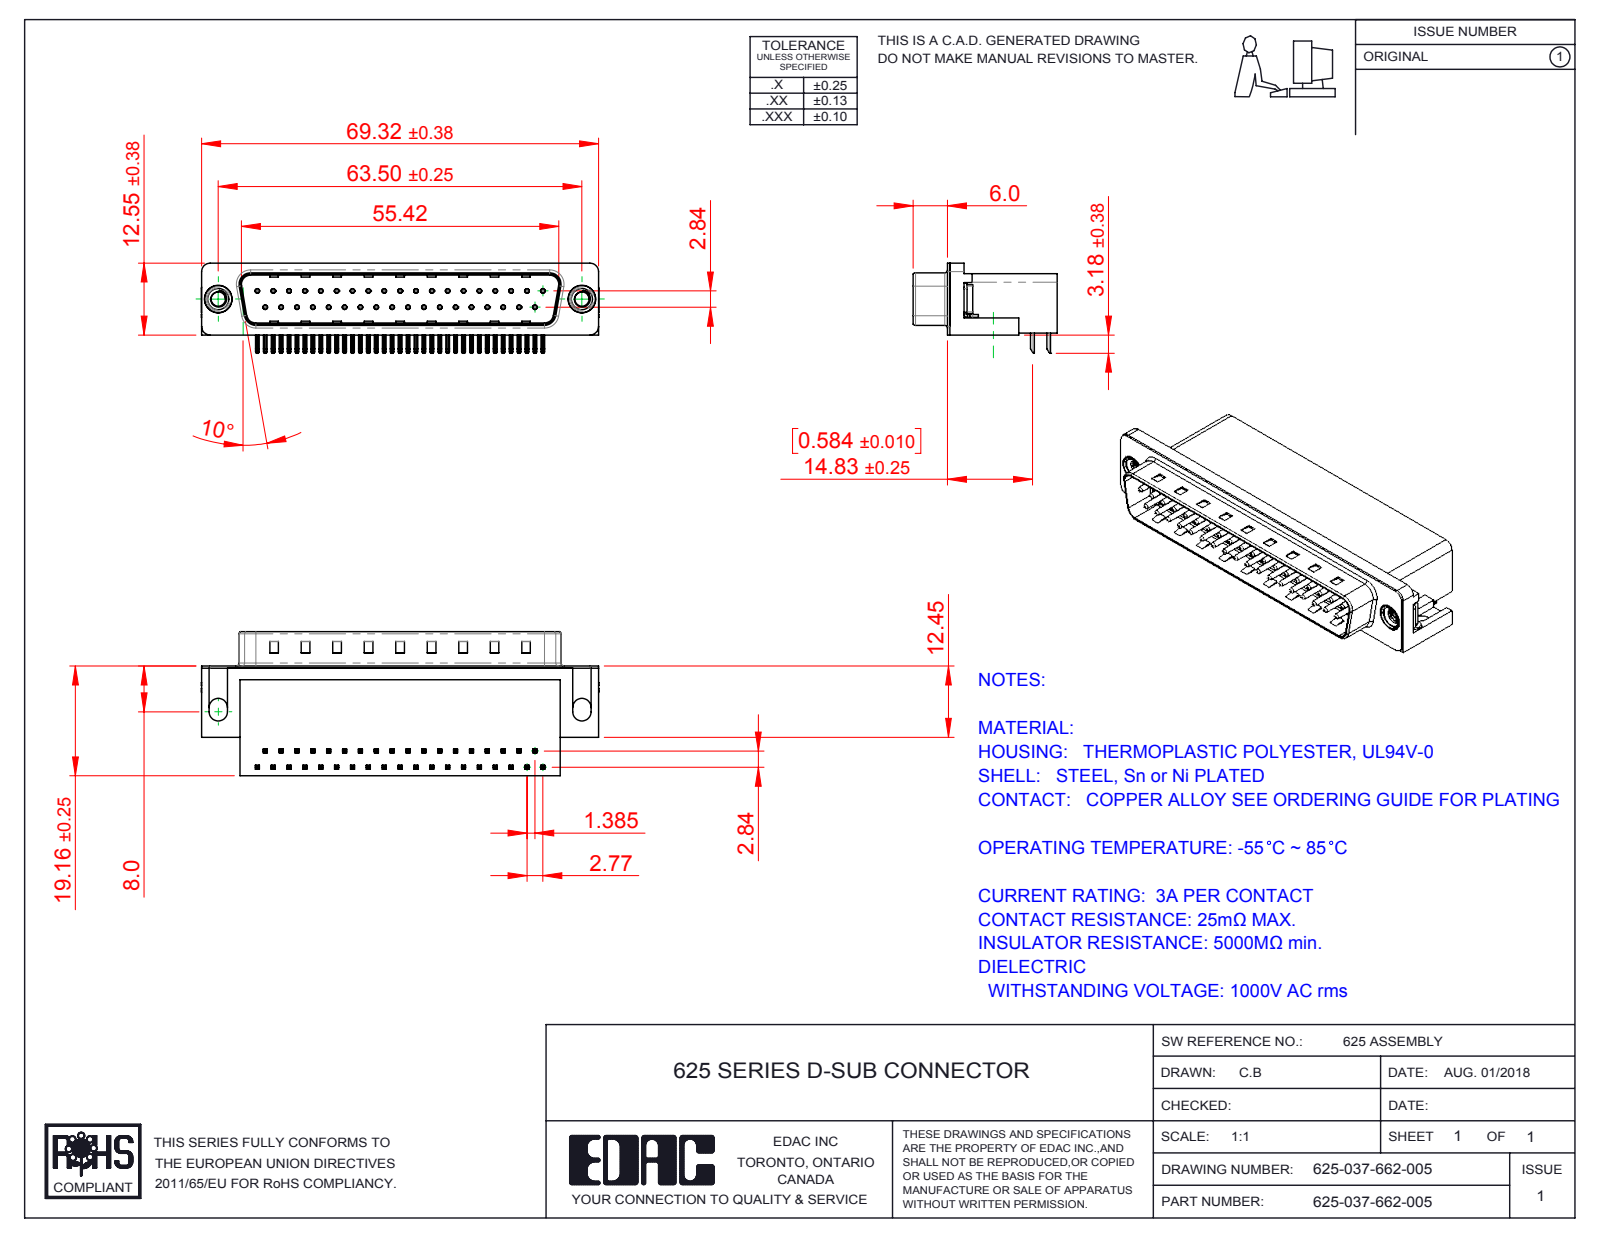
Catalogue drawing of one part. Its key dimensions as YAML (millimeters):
part_name: "625 Non Board Mount; 625-037-662-005; 625 Contact Bottom; 625 M3 Threaded Rivet (+3 more)"
step_written_by: "SolidWorks 2016 (CONFIG_CONTROL_DESIGN)"
units: millimeters
bodies: {solids: 43, faces: 3199, planar: 2015, cylindrical: 917, other: 267}
overall_size: [69.4, 25.16, 15.73]
volume: 12568
surface_area: 11623
round_holes:
  - {diameter: 0.35, count: 37}
  - {diameter: 0.8, count: 37}
  - {diameter: 2.5, count: 2}
  - {diameter: 4, count: 2}
  - {diameter: 4.8, count: 2}
  - {diameter: 5, count: 2}
round_bosses_or_shafts:
  - {diameter: 0.75, count: 37}
  - {diameter: 4.9, count: 2}
  - {diameter: 4.75, count: 2}
  - {diameter: 3.9, count: 2}
partial_cylinders:
  - {radius: 0.25, count: 156}
  - {radius: 0.12, count: 74}
  - {radius: 1, count: 16}
  - {radius: 0.5, count: 9}
  - {radius: 1.6, count: 8}
  - {radius: 1.5, count: 7}
  - {radius: 0.9, count: 4}
  - {radius: 2, count: 4}
face_to_face_distances: [10.34, 0.4, 18.76, 8.76, 19.16, 2.84, 2.09, 10.1, 1.74, 8.36]
hole_center_spacings: [3.16, 2.77, 5.54, 8.31, 11.08, 13.85, 19.39, 22.16]
